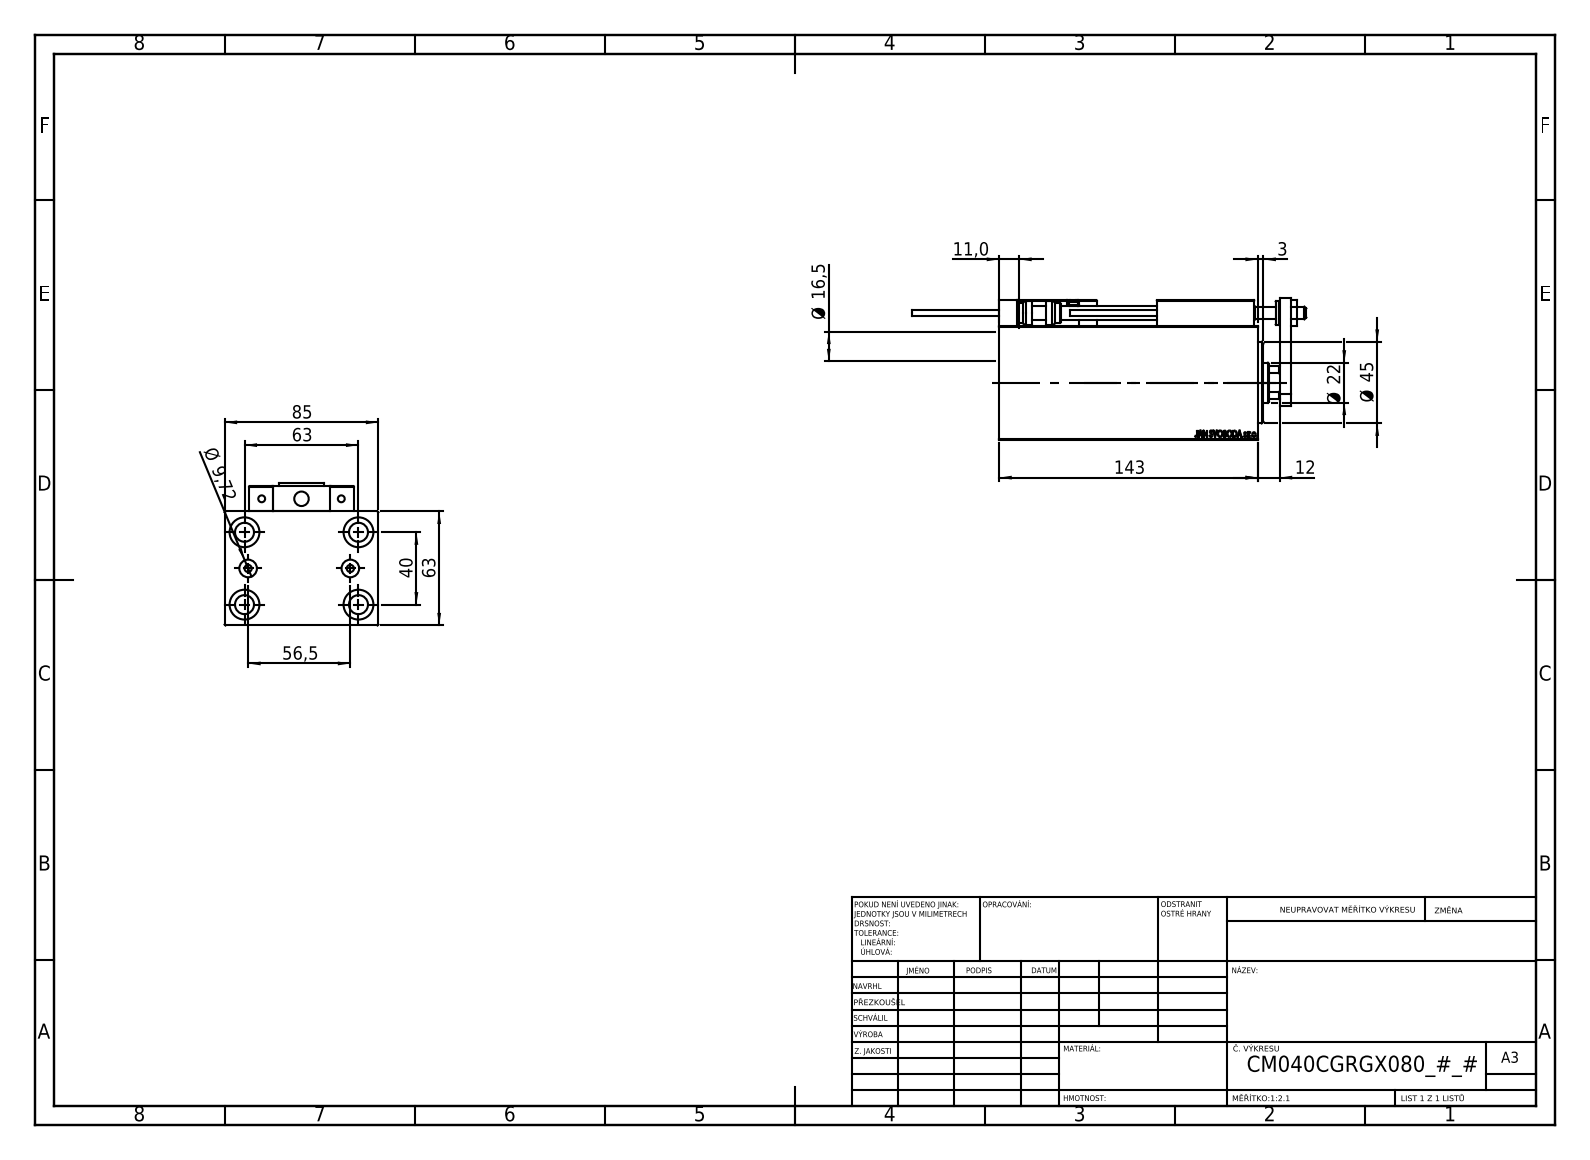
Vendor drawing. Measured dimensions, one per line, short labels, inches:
name: SWITCH DIM B,W; V450CM_C_VCP; SWITCH_X_FRONT_BACK; Block (+7 more)
written by: SolidWorks 2019 (CONFIG_CONTROL_DESIGN)
unit: in
bodies: 23 solids, 1278 faces (560 planar, 184 cylindrical, 534 other)
size: 8.571 × 3.346 × 3.091
volume: 41.89 in³; area: 217 in²
holes: 6× ⌀0.157, 5× ⌀0.315, 5× ⌀0.65, 4× ⌀0.126, 4× ⌀0.413, 2× ⌀0.197, 2× ⌀0.383, 1× ⌀0.276, 1× ⌀0.492, 1× ⌀0.866, 1× ⌀1.004, 1× ⌀1.575
bosses: 2× ⌀0.197, 2× ⌀0.15, 1× ⌀0.512, 1× ⌀0.433
rounds: 30× R0.012, 2× R0.118, 1× R0.413
face distances: 2.48, 3.346, 0.472, 5.157, 5.63, 0.551, 3.031, 0.591, 0.709, 1.181
hole spacings: 1.469, 0.448, 0.787, 0.791, 0.807, 1.165, 1.169, 1.42
